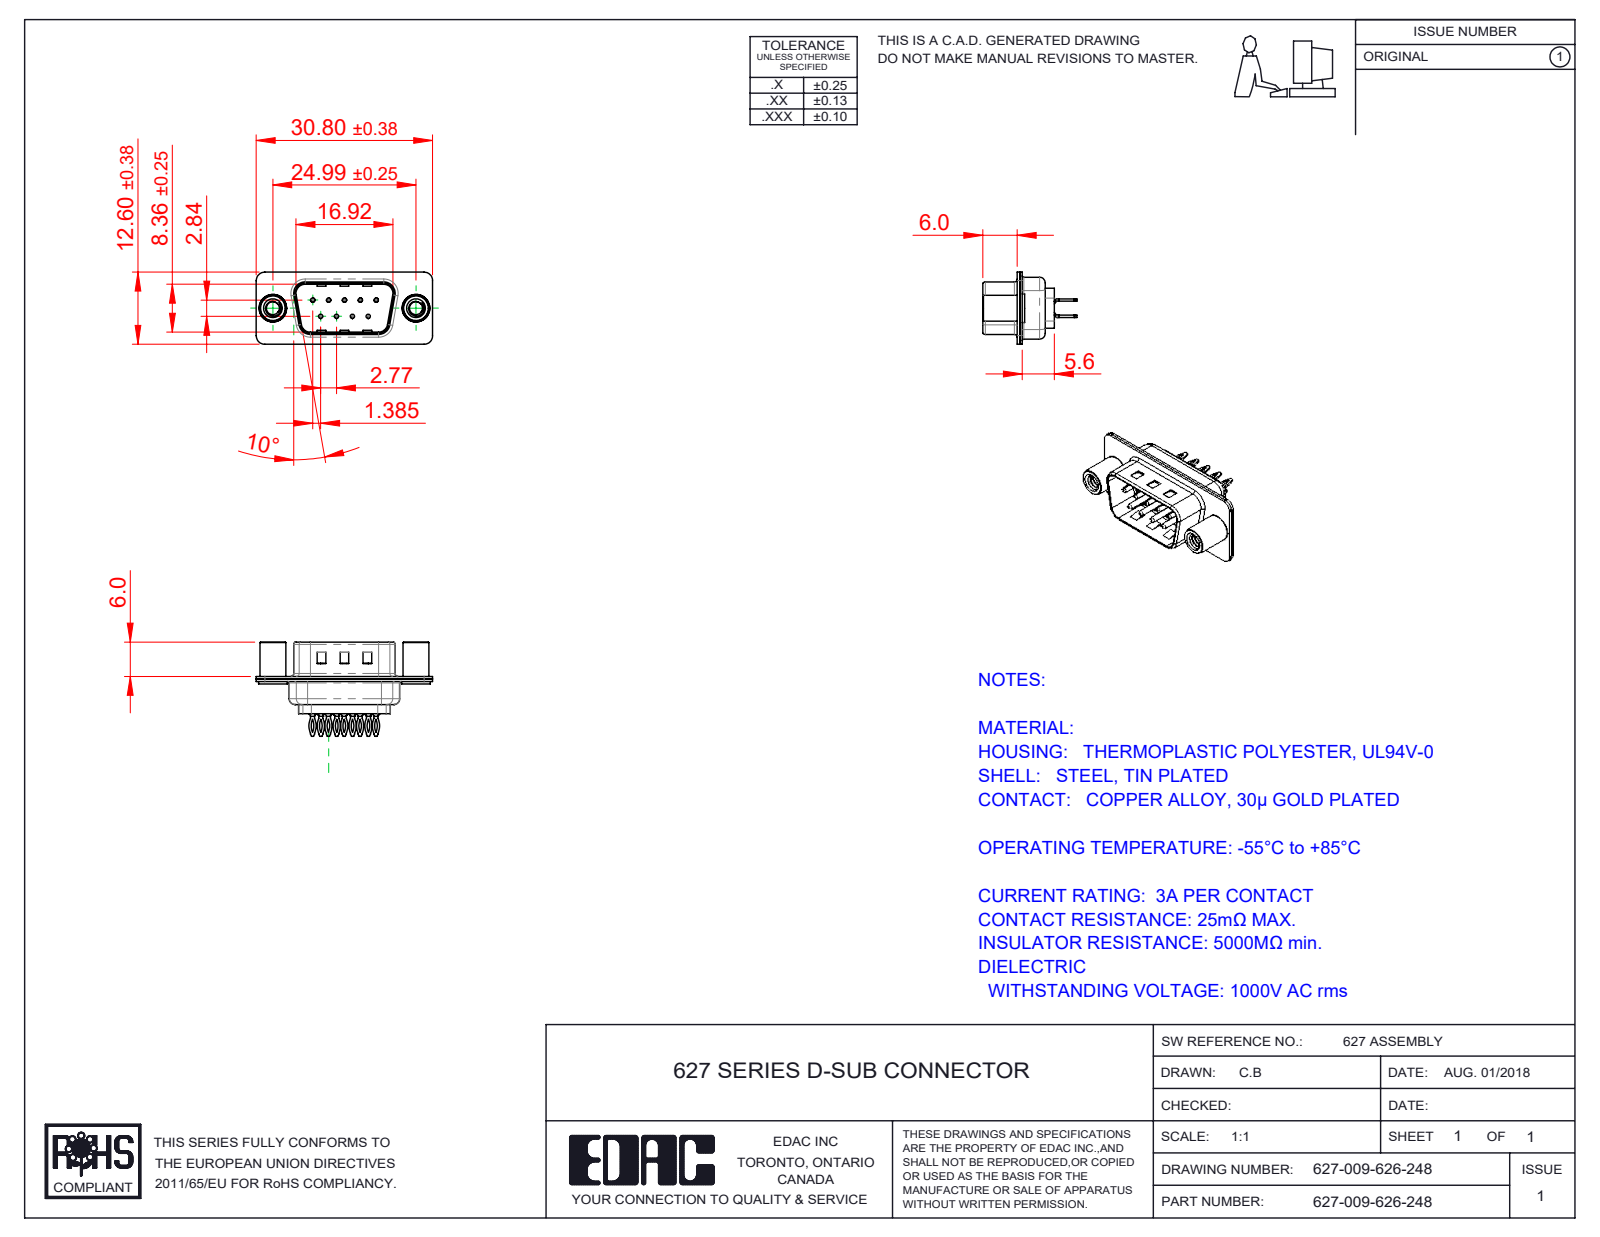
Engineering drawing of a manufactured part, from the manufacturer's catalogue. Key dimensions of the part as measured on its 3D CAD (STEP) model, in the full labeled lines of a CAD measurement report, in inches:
Part name (STEP PRODUCT): 627 Contact Row 2_26L; 627-009-626-248; 627 4-40 Threaded Standoff; 627 Housing_09 LP (+3 more)
STEP written by: SolidWorks 2020 (CONFIG_CONTROL_DESIGN)
Units: inches
Bodies: 14 solids, 1022 faces (289 planar, 436 cylindrical, 297 other)
Overall size (bounding box): 1.213 × 0.648 × 0.496
Volume: 0.084 in³ · Surface area: 6.355 in²
Round holes (diameter × count): ⌀0.014 ×9, ⌀0.043 ×9, ⌀0.063 ×9, ⌀0.089 ×2, ⌀0.157 ×2, ⌀0.189 ×2
Round bosses / shafts (diameter × count): ⌀0.079 ×9, ⌀0.059 ×9, ⌀0.03 ×9, ⌀0.197 ×2, ⌀0.193 ×2, ⌀0.177 ×2
Partial cylindrical surfaces — rounded edges, fillets, slot ends (radius × count): R0.059 ×18, R0.115 ×18, R0.131 ×18, R0.079 ×12, R0.02 ×8, R0.063 ×8, R0.01 ×4, R0.024 ×4
Main face-to-face distances: 0.016, 0.018, 0.035, 0.032, 0.377, 0.055, 0.345, 0.02, 0.059, 0.238
Hole centre spacings: 0.124, 0.109, 0.218, 0.198, 0.198, 0.327, 0.294, 0.295
